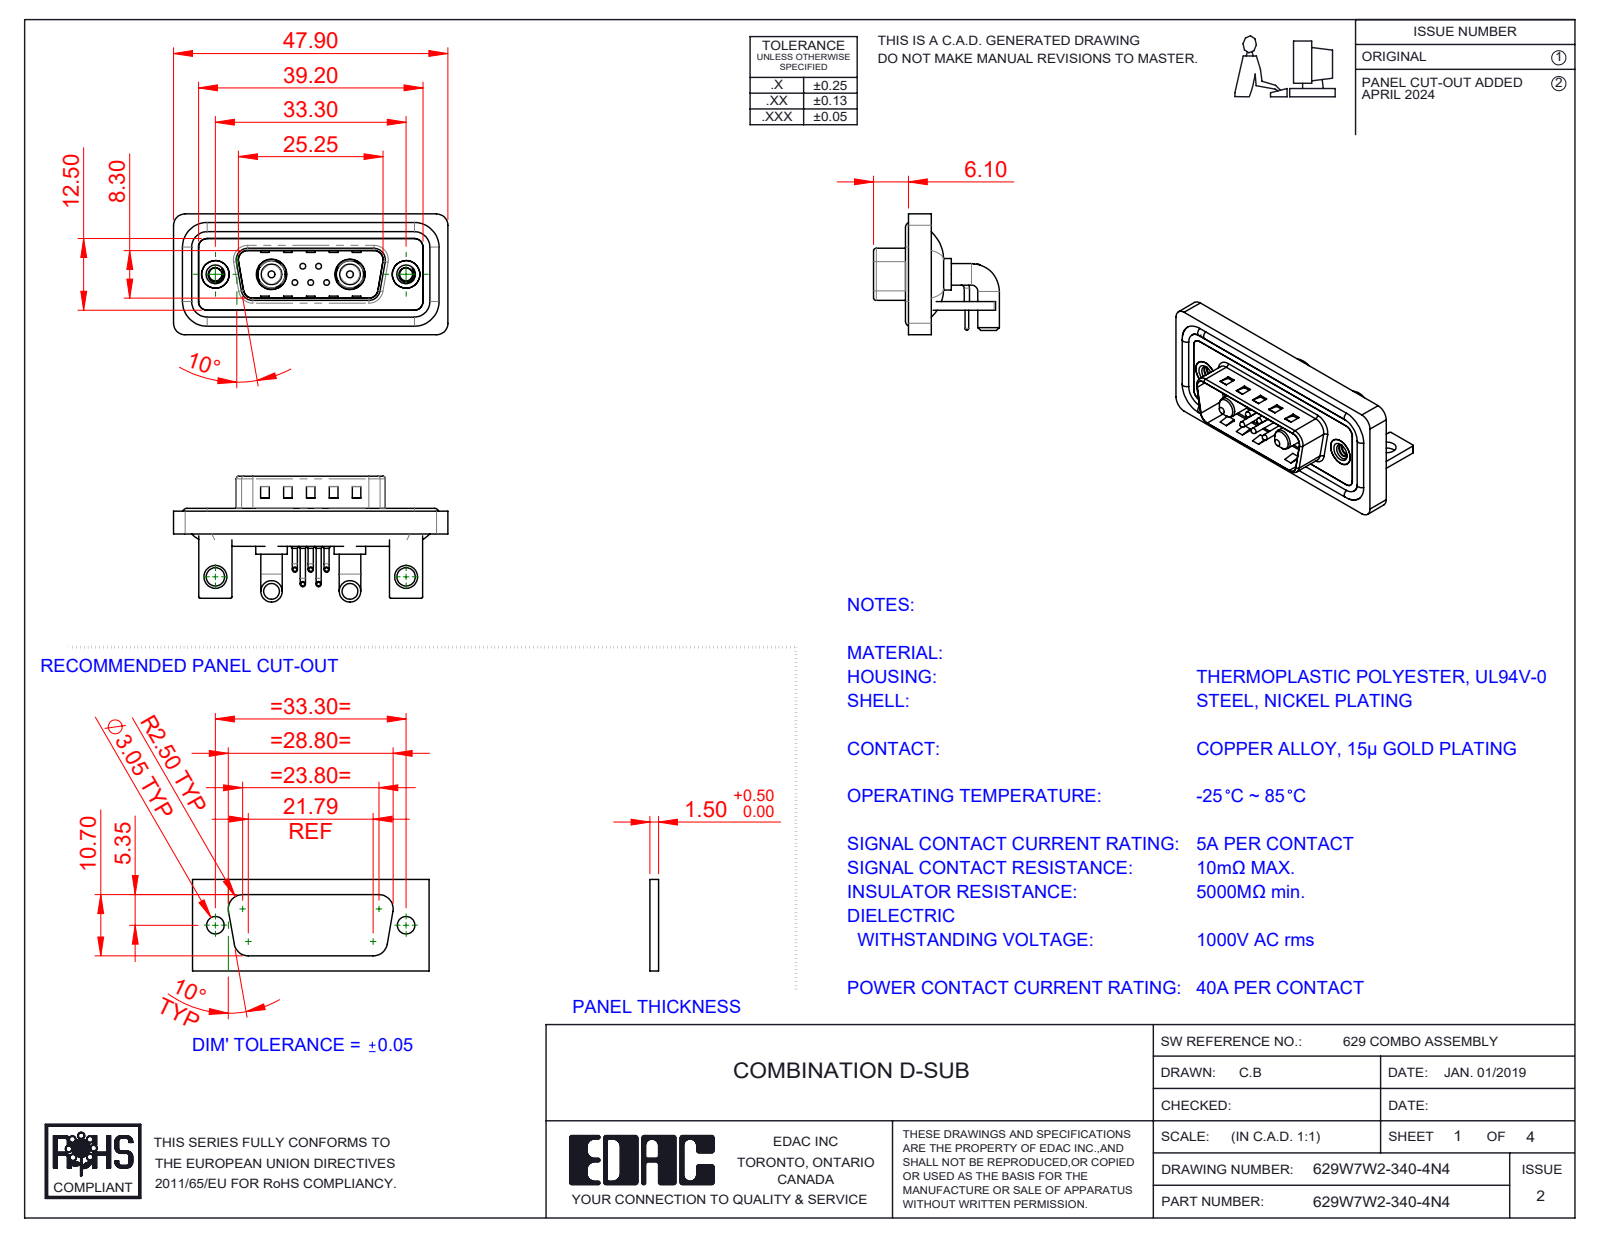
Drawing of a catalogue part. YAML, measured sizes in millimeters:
part_name: "629Combo Contact Row 1; 629Combo Shell Front_15 Contacts; 629Combo Housing_7W2; 629Combo Stabilizer Bracket (+6 more)"
step_written_by: "SolidWorks 2023 (CONFIG_CONTROL_DESIGN)"
units: millimeters
bodies: {solids: 18, faces: 1123, planar: 537, cylindrical: 424, other: 162}
overall_size: [47.9, 21.98, 21.1]
volume: 6104
surface_area: 9815
round_holes:
  - {diameter: 0.75, count: 5}
  - {diameter: 1.6, count: 5}
  - {diameter: 2, count: 5}
  - {diameter: 2.26, count: 2}
  - {diameter: 3.2, count: 2}
  - {diameter: 4, count: 2}
  - {diameter: 4.8, count: 2}
  - {diameter: 4.85, count: 2}
  - {diameter: 5, count: 2}
  - {diameter: 5.3, count: 2}
round_bosses_or_shafts:
  - {diameter: 0.9, count: 10}
  - {diameter: 1.5, count: 5}
  - {diameter: 1, count: 5}
  - {diameter: 0.65, count: 5}
  - {diameter: 3.75, count: 4}
  - {diameter: 1.6, count: 4}
  - {diameter: 5.5, count: 2}
  - {diameter: 5.2, count: 2}
partial_cylinders:
  - {radius: 2, count: 21}
  - {radius: 1.5, count: 18}
  - {radius: 0.25, count: 16}
  - {radius: 0.5, count: 9}
  - {radius: 1.6, count: 8}
  - {radius: 1.01, count: 5}
  - {radius: 0.6, count: 4}
  - {radius: 0.65, count: 4}
face_to_face_distances: [0.4, 1.5, 0.8, 2.9, 2.1, 1.1, 1.6, 1.2, 3.7, 4.5]
hole_center_spacings: [3.16, 2.77, 9.8, 23.5, 33.3, 4.31, 4.33, 5.03]
